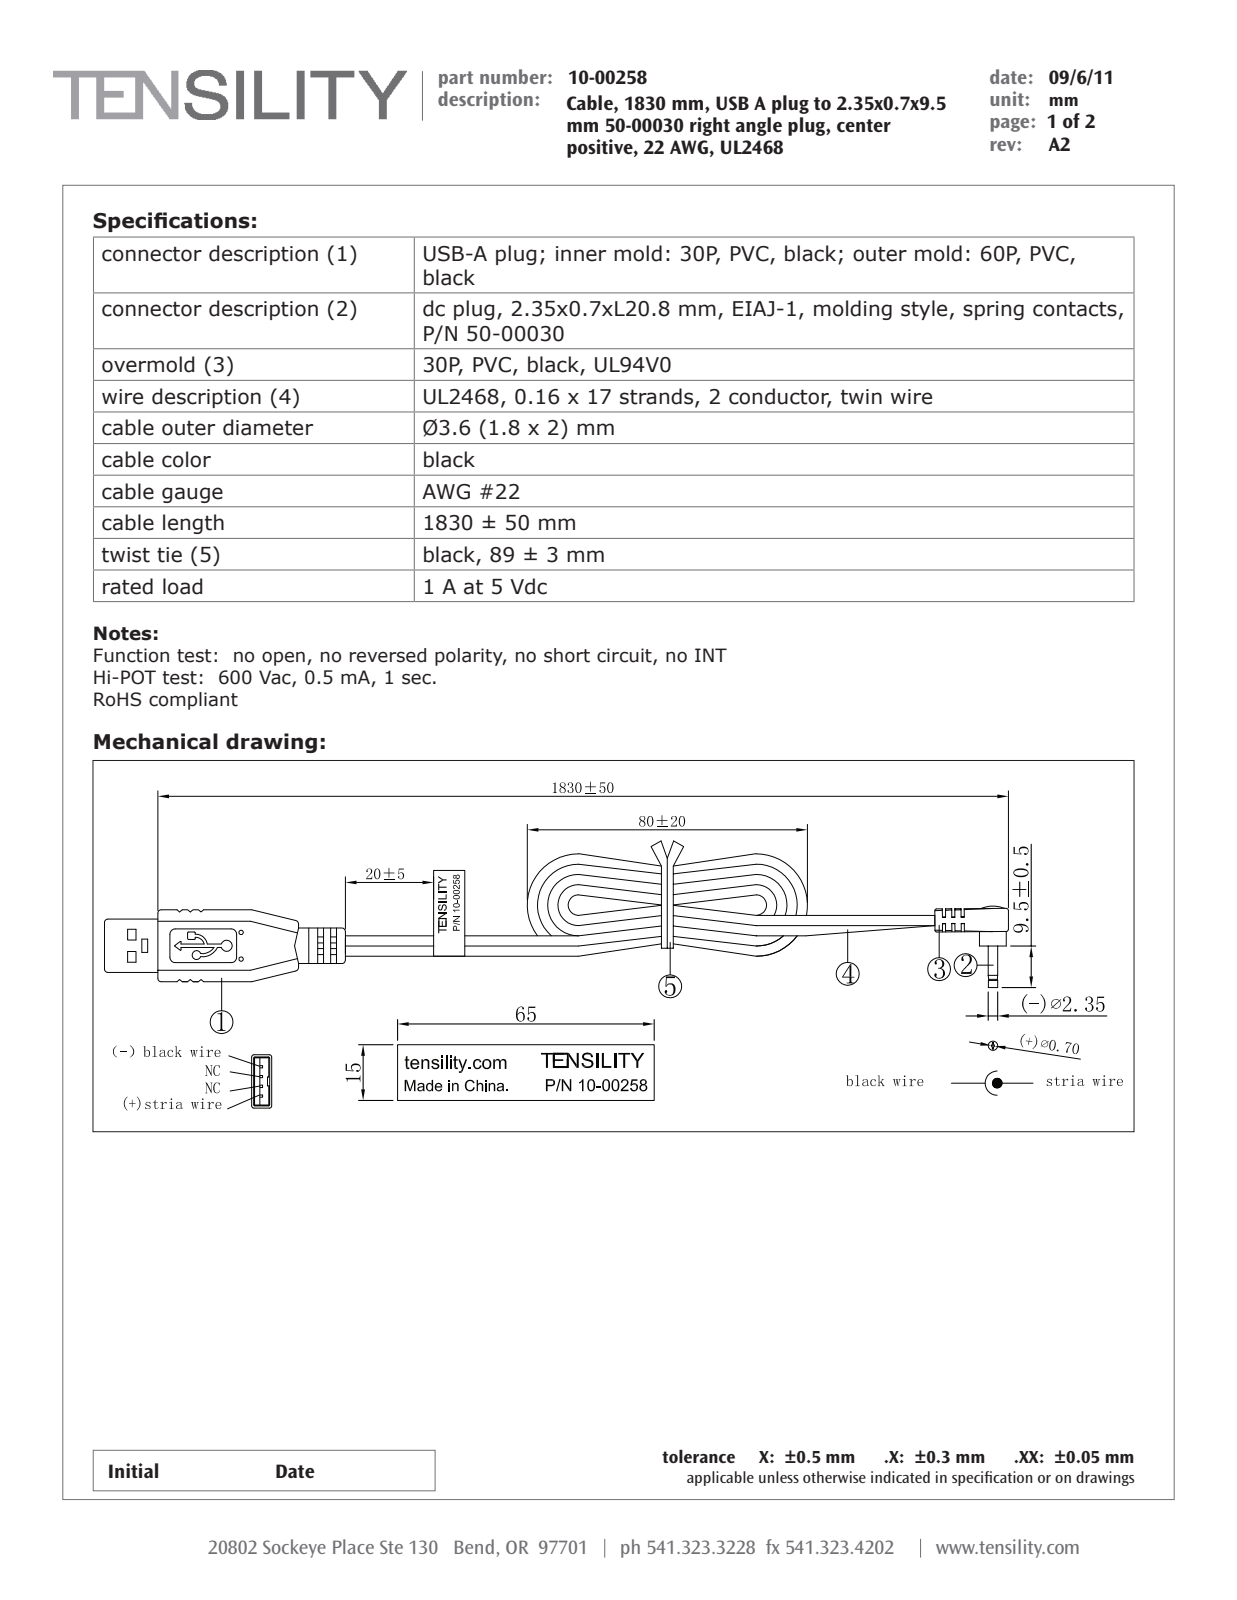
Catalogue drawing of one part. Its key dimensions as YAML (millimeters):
part_name: "50-00425 shell; 50-00030 shell; 30-00008_wbc; 50-00030 insulator (+8 more)"
step_written_by: "SolidWorks 2015 (AUTOMOTIVE_DESIGN)"
units: millimeters
bodies: {solids: 60, faces: 1243, planar: 602, cylindrical: 320, other: 321}
overall_size: [209.5, 47.8, 8.4]
volume: 7219
surface_area: 12520
round_holes:
  - {diameter: 0.85, count: 2}
  - {diameter: 0.7, count: 1}
  - {diameter: 0.8, count: 1}
  - {diameter: 1.2, count: 1}
  - {diameter: 1.2, count: 1}
  - {diameter: 1.95, count: 1}
  - {diameter: 3.82, count: 1}
round_bosses_or_shafts:
  - {diameter: 1.9, count: 2}
  - {diameter: 8, count: 1}
  - {diameter: 7.26, count: 1}
  - {diameter: 4.63, count: 1}
  - {diameter: 4.5, count: 1}
  - {diameter: 4.1, count: 1}
  - {diameter: 4, count: 1}
  - {diameter: 2.38, count: 1}
partial_cylinders:
  - {radius: 0.1, count: 50}
  - {radius: 0.2, count: 24}
  - {radius: 0.5, count: 14}
  - {radius: 0.25, count: 8}
  - {radius: 0.75, count: 8}
  - {radius: 0.3, count: 4}
  - {radius: 0.4, count: 4}
  - {radius: 0.64, count: 4}
face_to_face_distances: [1.95, 1.86, 1.81, 2.01, 6.45, 2.33, 3.87, 2.06, 0.32, 4.28]
hole_center_spacings: [1.78]
